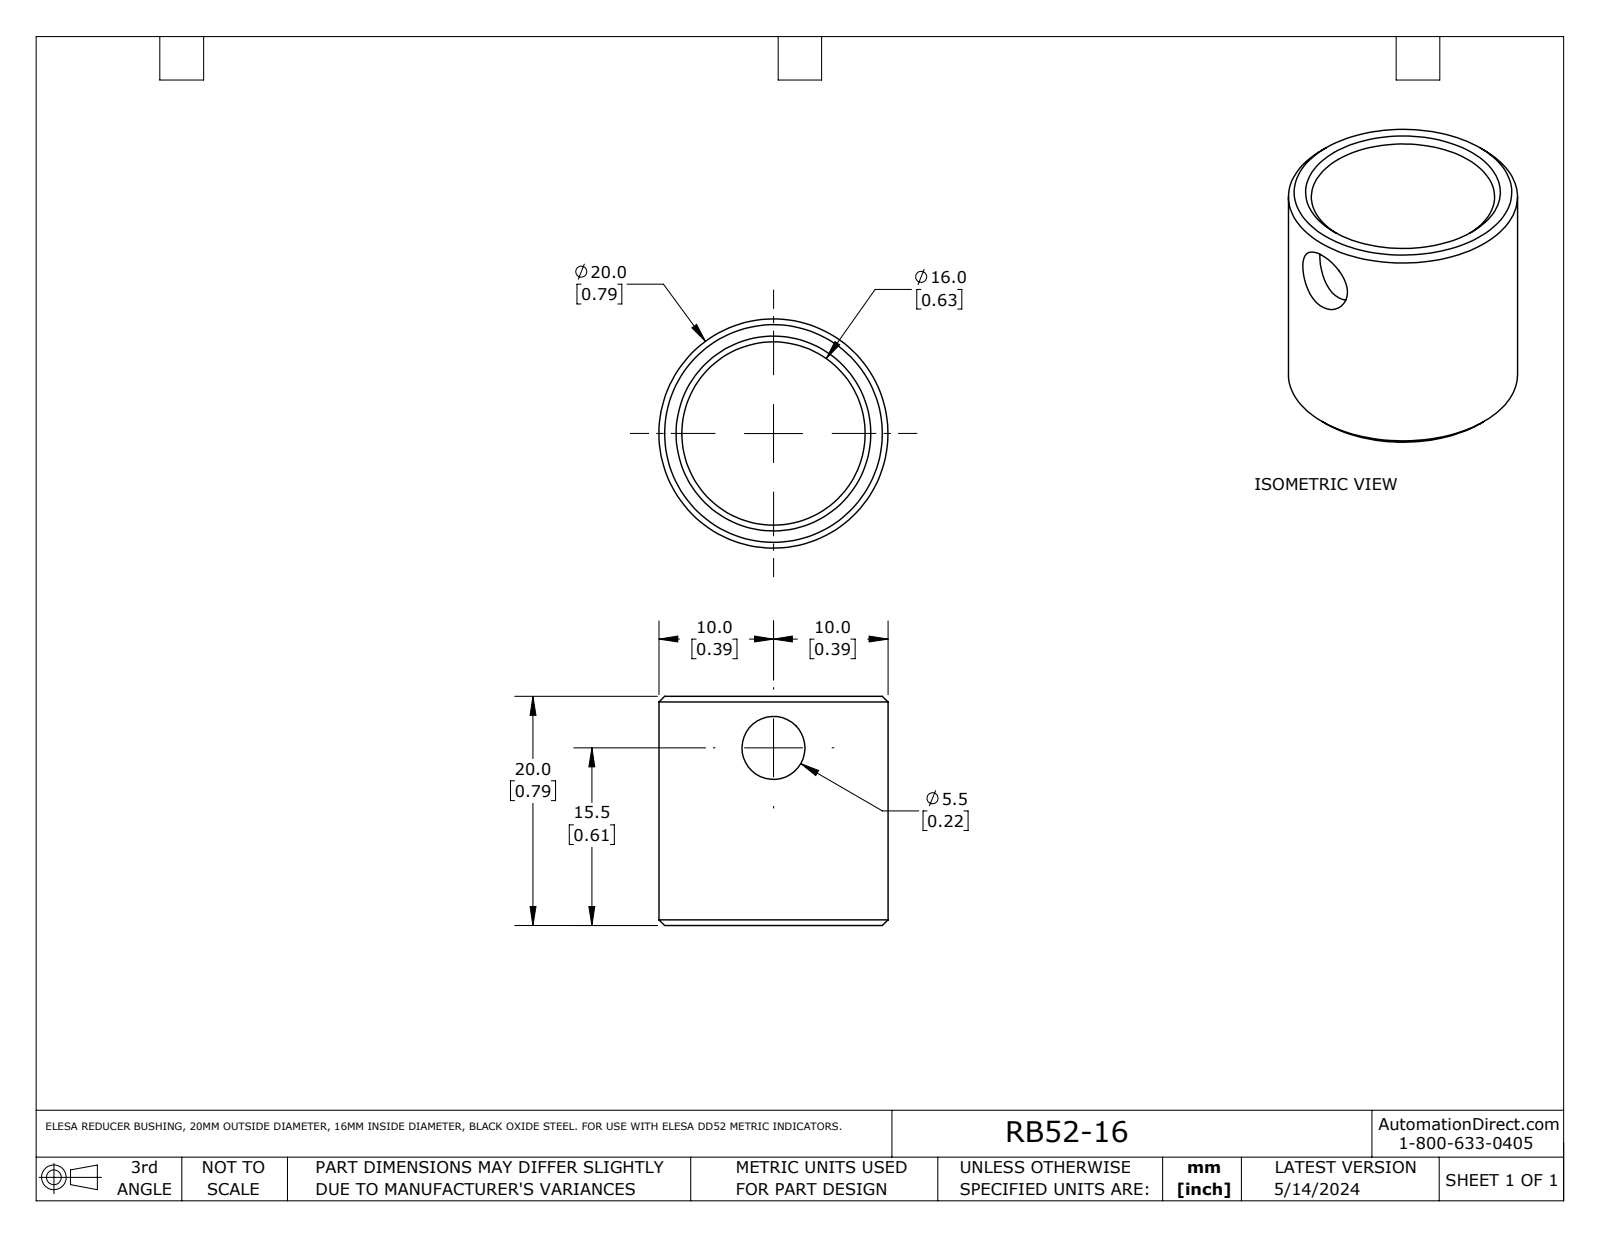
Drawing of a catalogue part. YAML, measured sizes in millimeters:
part_name: "RB52-16"
step_written_by: "SolidWorks 2023 (AUTOMOTIVE_DESIGN)"
units: millimeters
bodies: {solids: 1, faces: 9, planar: 2, cylindrical: 3, other: 4}
overall_size: [20, 20, 20]
volume: 2180
surface_area: 2409
round_holes:
  - {diameter: 5.5, count: 1}
  - {diameter: 16, count: 1}
round_bosses_or_shafts:
  - {diameter: 20, count: 1}
face_to_face_distances: [20]
